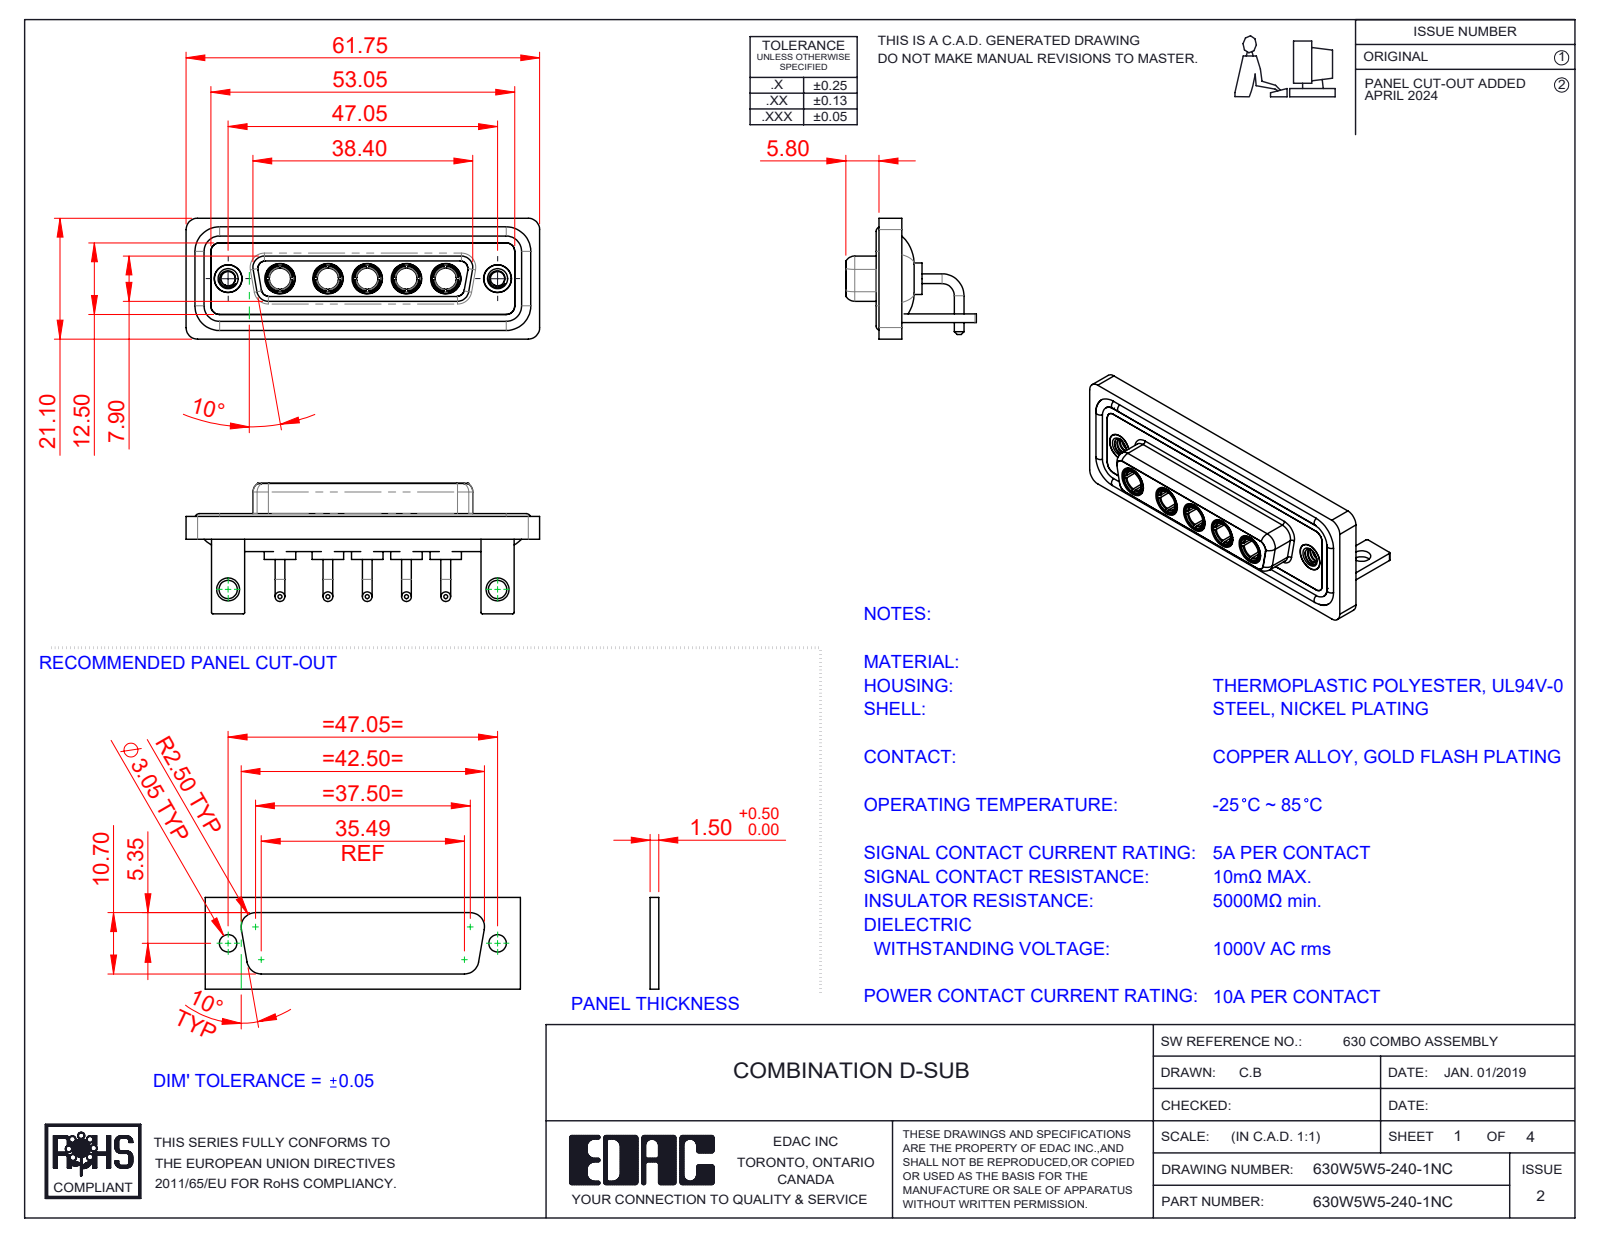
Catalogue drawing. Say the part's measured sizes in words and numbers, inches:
The part is named "630W5W5-240-1NC; 630Combo Shell Front_25 Contacts; 630Combo Stabilizer Bracket_50 Contacts; 630Combo Shell Rear_25 Contacts (+4 more)". Its 3-D file was written by "SolidWorks 2023 (CONFIG_CONTROL_DESIGN)". It is 19 solids with 818 faces: 270 planar, 335 cylindrical and 213 other. Overall it measures 2.431 by 0.898 by 0.831 inches. Its volume is 0.519 cubic inches and its surface area 22.16 square inches. Round holes: 7 of diameter 0.191, 5 of diameter 0.146, 5 of diameter 0.209, 2 of diameter 0.098, 2 of diameter 0.126, 2 of diameter 0.157, 2 of diameter 0.159, 2 of diameter 0.197. Round bosses or shafts: 10 of diameter 0.067, 5 of diameter 0.217, 5 of diameter 0.205, 5 of diameter 0.195, 5 of diameter 0.187, 5 of diameter 0.148, 4 of diameter 0.063, 2 of diameter 0.195. Partial cylindrical surfaces (rounded edges, fillets, slot ends): 19 of radius 0.079, 18 of radius 0.059, 16 of radius 0.01, 8 of radius 0.053, 8 of radius 0.063, 5 of radius 0.02, 5 of radius 0.083, 4 of radius 0.024. The main face-to-face distances are 0.016, 0.071, 0.059, 0.114, 0.146, 0.161, 0.043, 0.055, 0.063, 0.098. The hole center spacings are 0.27, 0.356, 1.496, 1.852, 0.27, 0.33, 0.54, 0.541.
